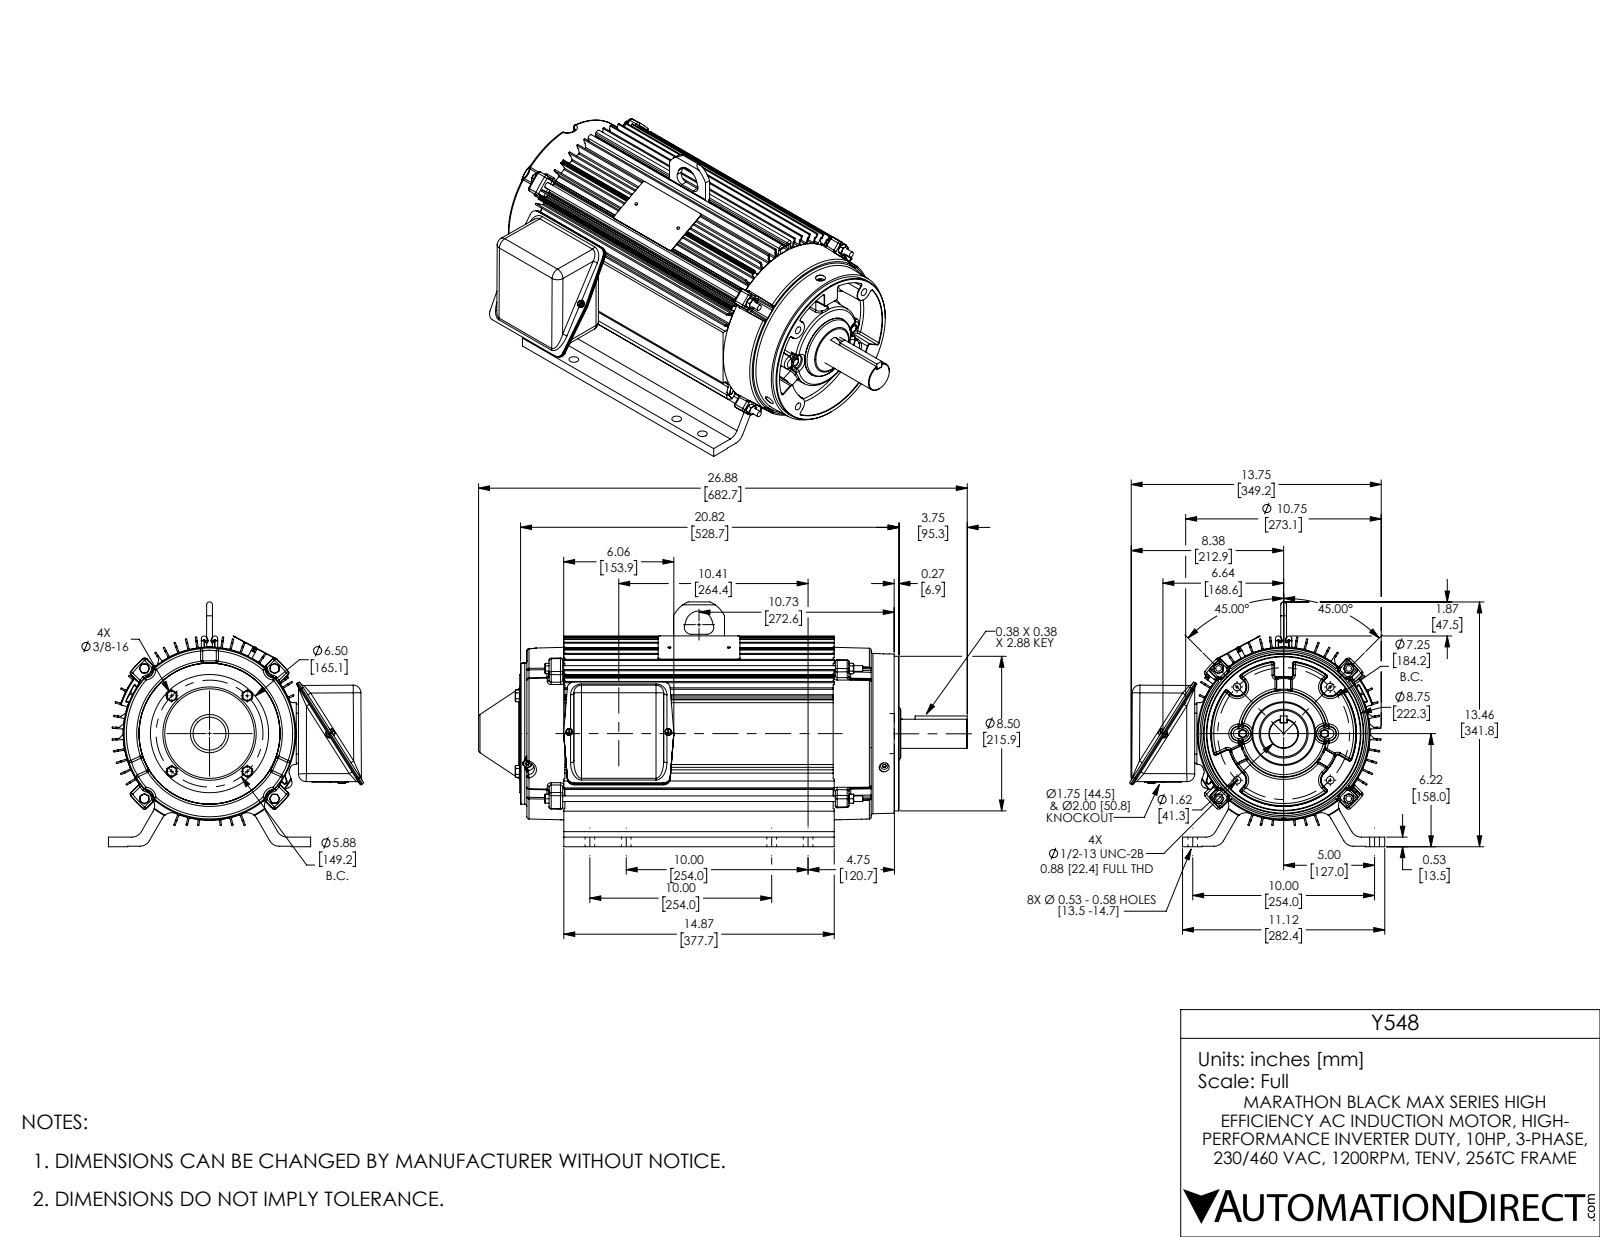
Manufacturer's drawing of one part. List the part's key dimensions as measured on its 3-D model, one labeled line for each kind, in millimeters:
Part name (STEP PRODUCT): Y548
STEP written by: SolidWorks 2021 (AUTOMOTIVE_DESIGN)
Units: millimetres
Bodies: 39 solids, 3070 faces (752 planar, 853 cylindrical, 1465 other)
Overall size (bounding box): 682.7 × 356.6 × 341.9
Volume: 6 396 000 mm³ · Surface area: 2 076 000 mm²
Round holes (diameter × count): ⌀8.7 ×10, ⌀13.5 ×8, ⌀6.4 ×5, ⌀12.7 ×5, ⌀6.5 ×4, ⌀7.9 ×4, ⌀10.3 ×4, ⌀10.7 ×4, ⌀11.2 ×4, ⌀4.5 ×2, ⌀5.1 ×2, ⌀7.1 ×2
Round bosses / shafts (diameter × count): ⌀9.7 ×5, ⌀12.7 ×4, ⌀9.5 ×4, ⌀7.9 ×4, ⌀10.1 ×2, ⌀6.4 ×2, ⌀4.8 ×2, ⌀2.1 ×2
Partial cylindrical surfaces — rounded edges, fillets, slot ends (radius × count): R3 ×134, R1.5 ×74, R2.5 ×54, R1 ×32, R9.7 ×29, R0.8 ×15, R4.6 ×12, R1.6 ×8
Main face-to-face distances: 1.9, 1.5, 16, 484.7, 13.5, 3, 1.9, 0.8, 5.1, 12.7
Hole centre spacings: 118.5, 148.6, 148.7, 158.1, 158.2, 181.8, 254, 55.5
